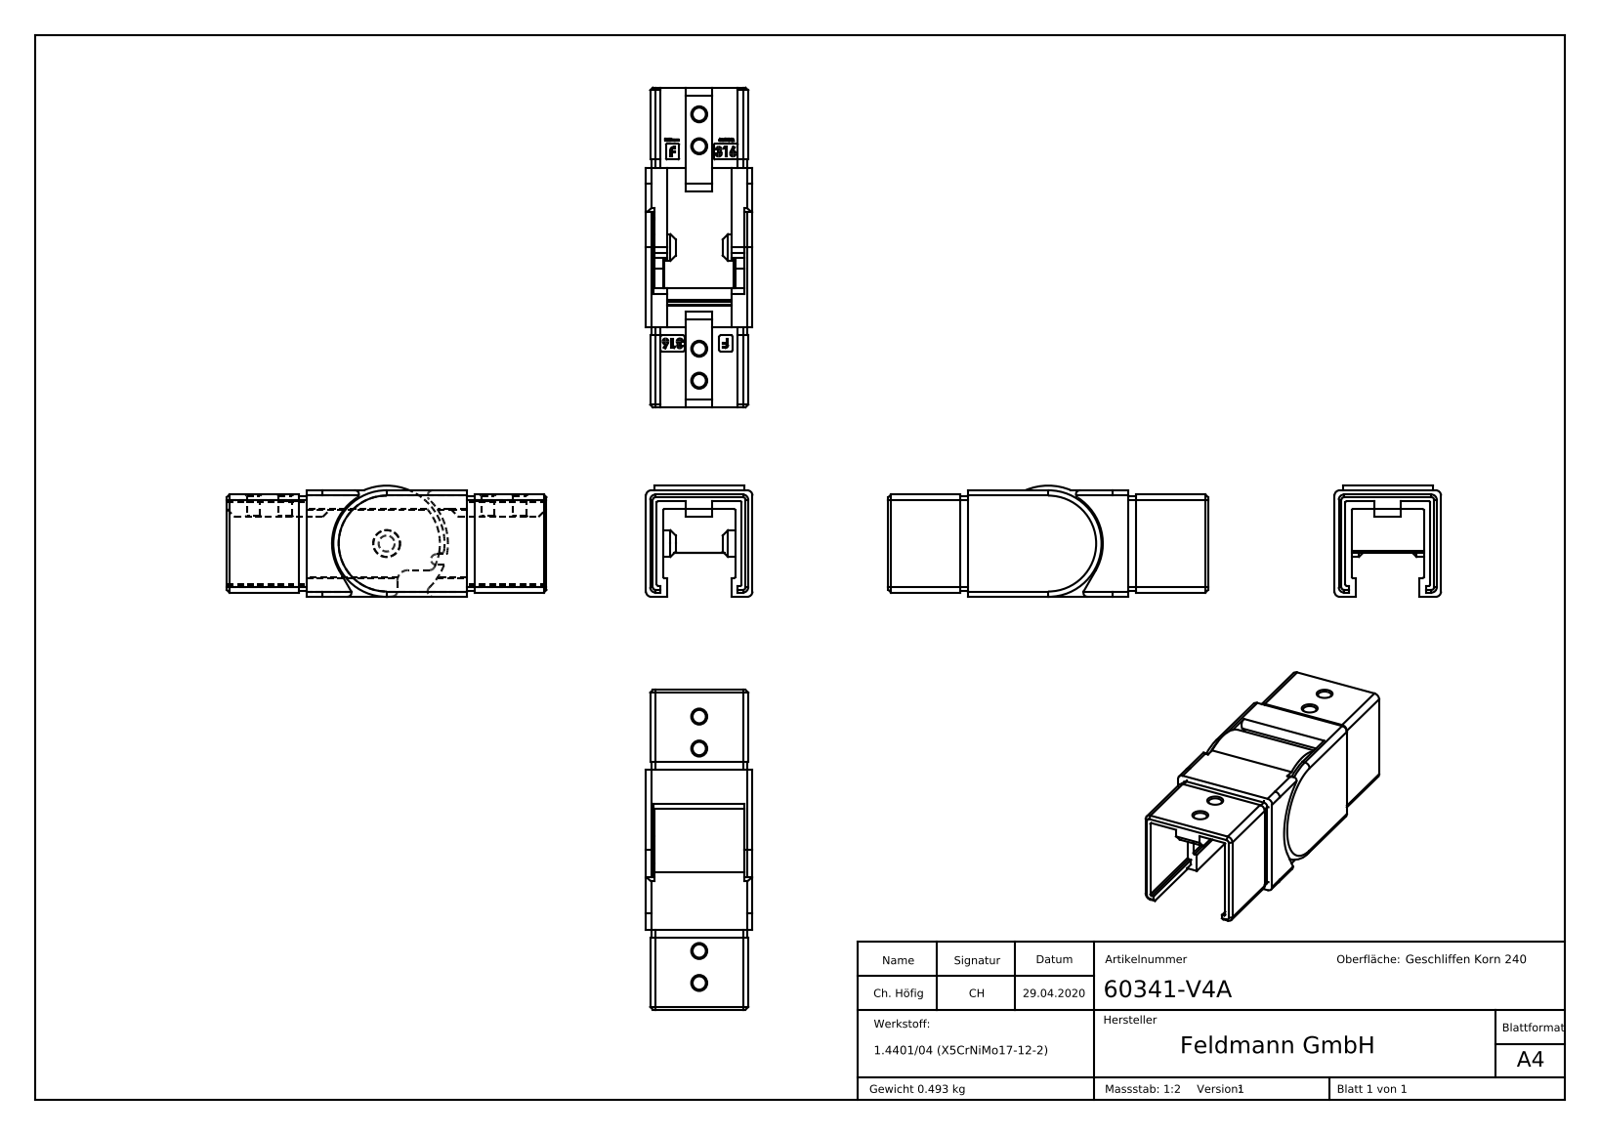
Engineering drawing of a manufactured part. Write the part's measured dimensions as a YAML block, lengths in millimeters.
part_name: "60341-V4A; 60341-V4A Teil1_60341-V4A Teil1; 60341-V4A Teil2_60341-V4A Teil2; 60341-V4A Teil1 (+1 more)"
step_written_by: "SolidWorks 2015 (CONFIG_CONTROL_DESIGN)"
units: millimeters
bodies: {solids: 2, faces: 577, planar: 332, cylindrical: 99, other: 146}
overall_size: [120, 41.75, 40]
volume: 61637
surface_area: 36891
round_holes:
  - {diameter: 5, count: 4}
  - {diameter: 10.1, count: 1}
round_bosses_or_shafts:
  - {diameter: 10, count: 1}
partial_cylinders:
  - {radius: 0.5, count: 24}
  - {radius: 2, count: 13}
  - {radius: 1.5, count: 6}
  - {radius: 1, count: 1}
  - {radius: 4, count: 1}
  - {radius: 20, count: 1}
  - {radius: 20.5, count: 1}
  - {radius: 21.75, count: 1}
face_to_face_distances: [2.5, 4.1, 1.6, 35.9, 38.4, 34.3, 3, 1.4, 32.9, 4.9]
hole_center_spacings: [12, 88, 76, 100]
